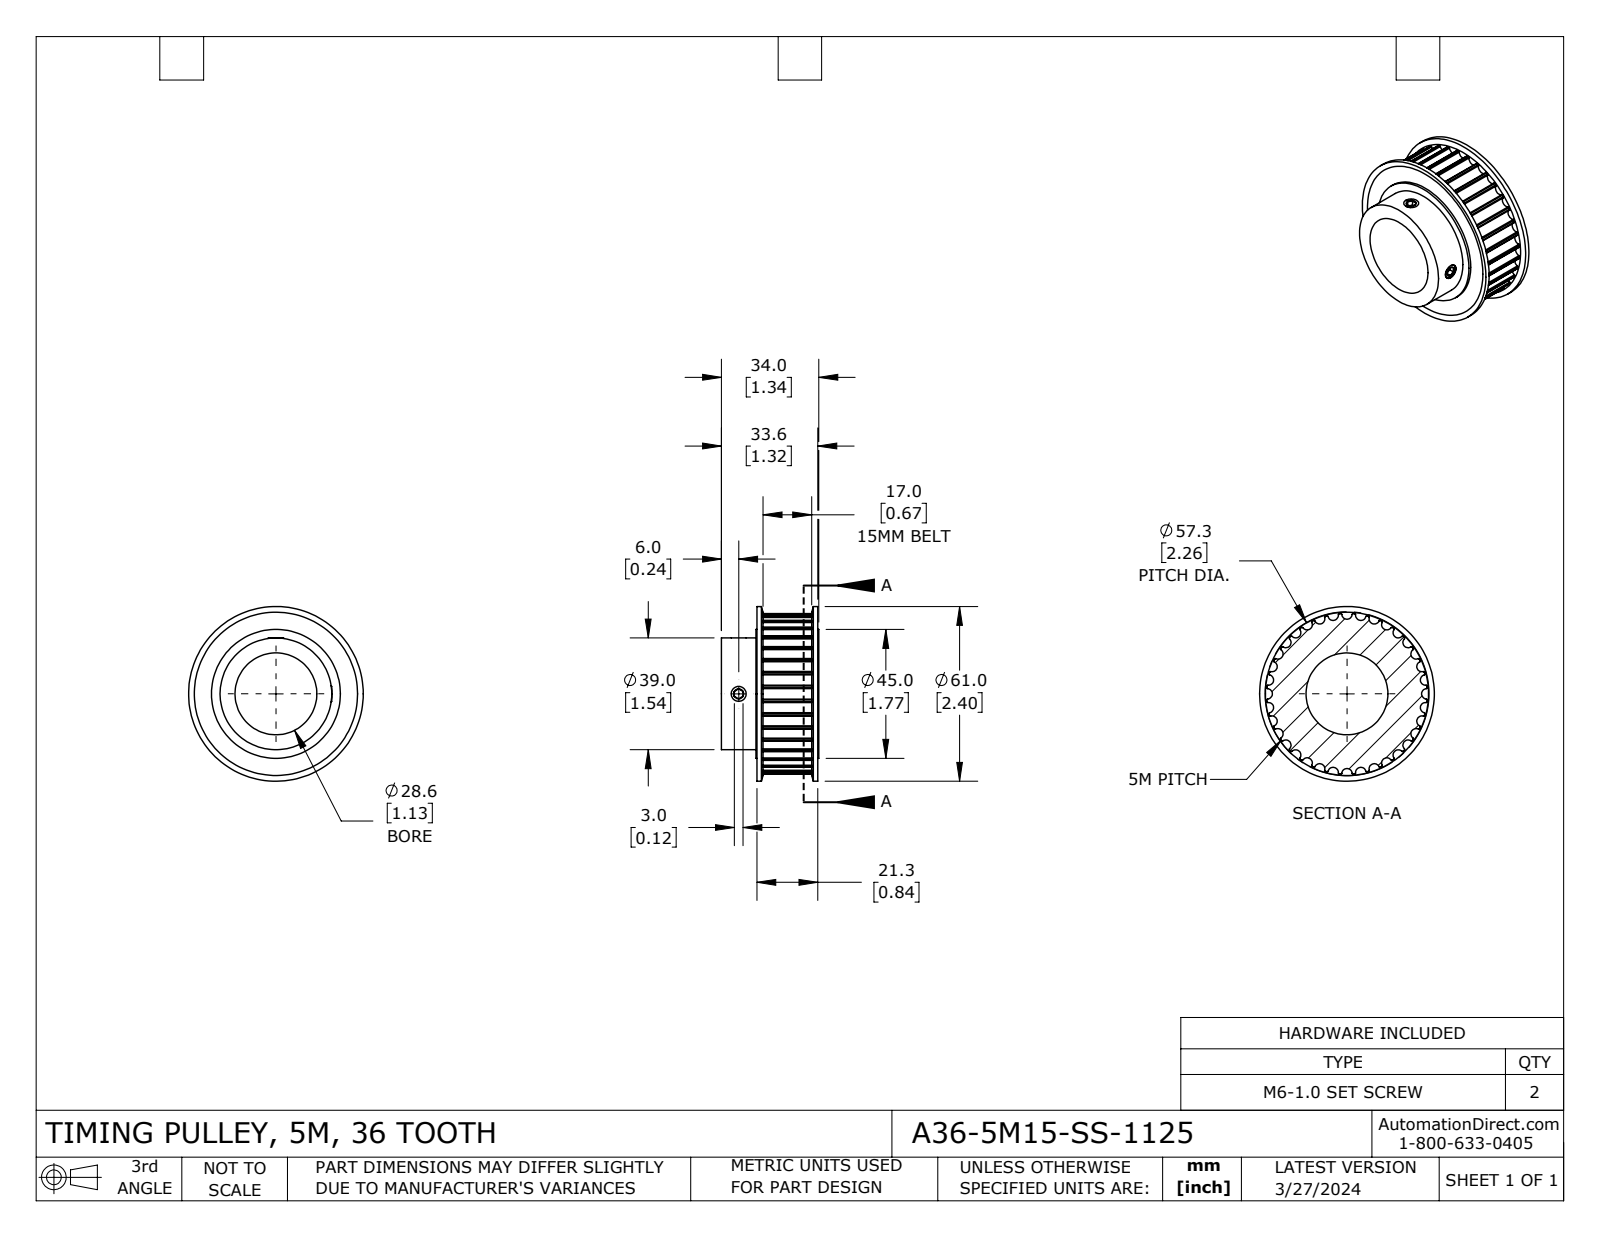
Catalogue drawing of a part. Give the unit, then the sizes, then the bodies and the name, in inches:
Units: inches
Overall size (bounding box): 2.402 × 2.402 × 1.339
Round holes (diameter × count): ⌀0.197 ×2, ⌀1.125 ×1, ⌀1.772 ×1
Round bosses / shafts (diameter × count): ⌀0.236 ×2, ⌀2.402 ×1, ⌀1.535 ×1
Partial cylindrical surfaces — rounded edges, fillets, slot ends (radius × count): R0.012 ×72, R0.072 ×36, R1.105 ×1
Main face-to-face distances: 0.063, 0.732, 0.669, 0.035, 0.098, 0.768, 0.831, 0.795, 1.339, 1.303
Volume: 2.639 in³ · Surface area: 30.35 in²
Bodies: 5 solids, 262 faces (25 planar, 203 cylindrical, 34 other)
Part name (STEP PRODUCT): A36-5M15-SS-1125
STEP written by: SolidWorks 2021 (CONFIG_CONTROL_DESIGN)
